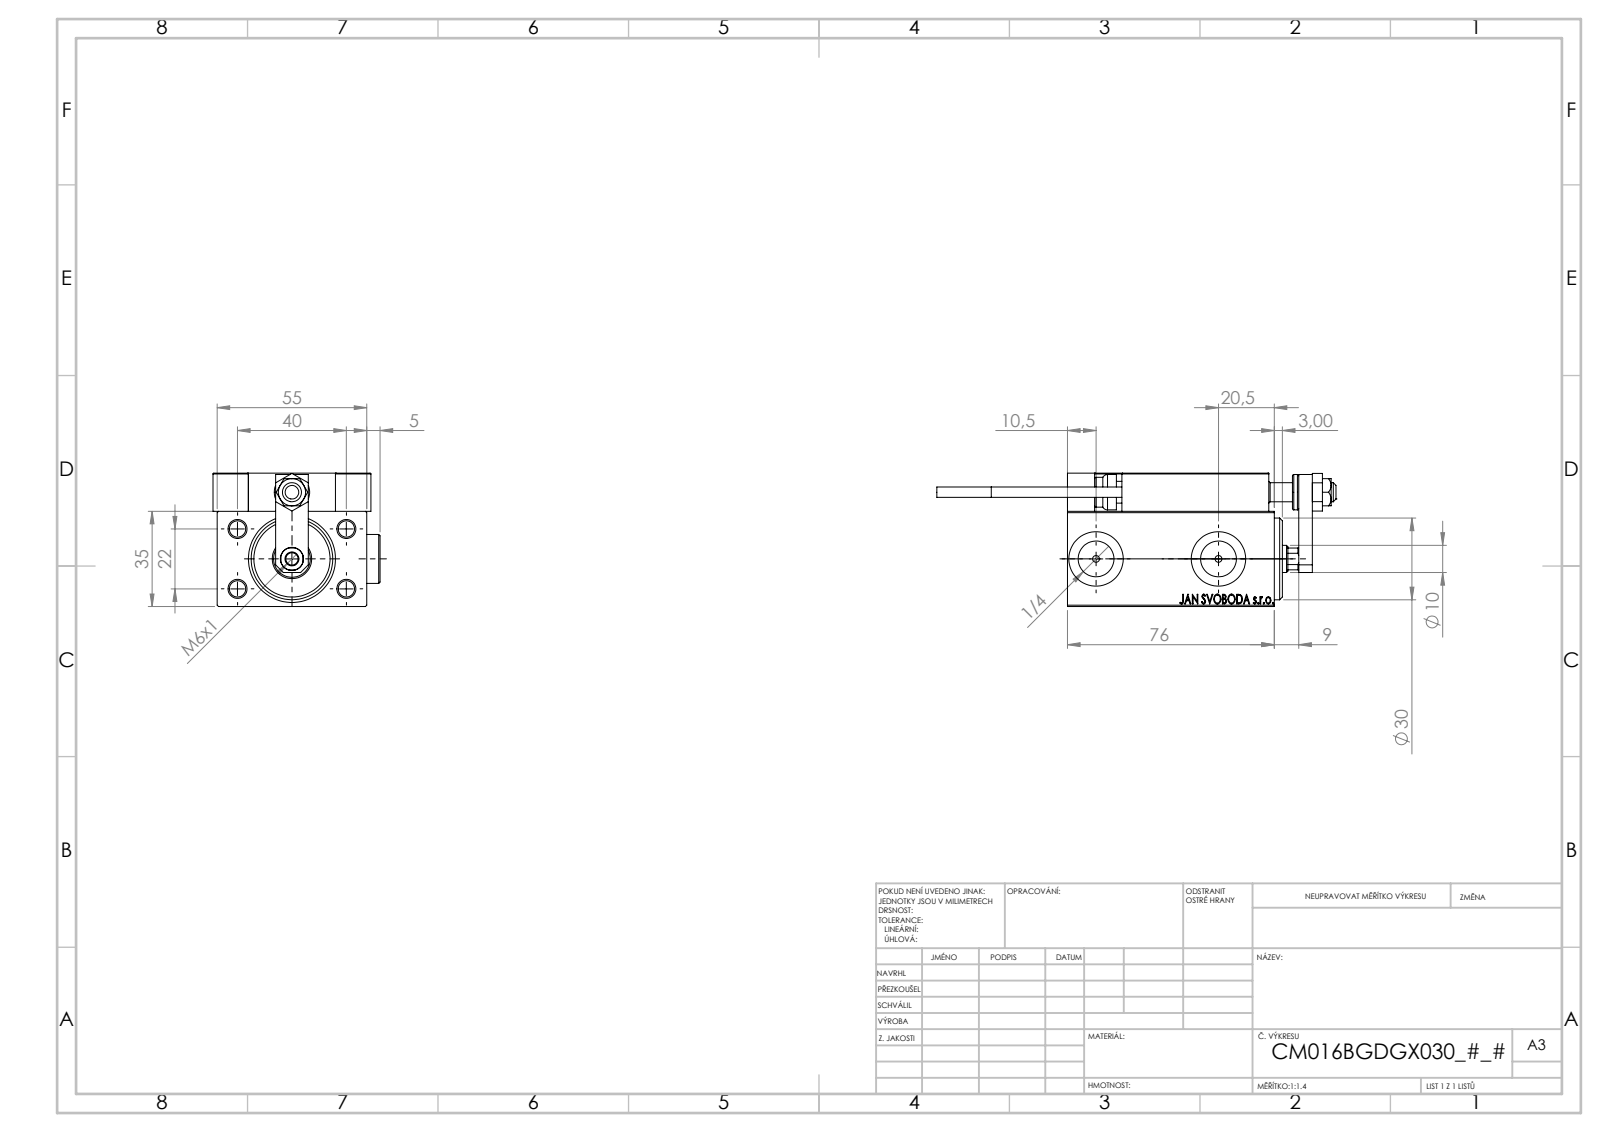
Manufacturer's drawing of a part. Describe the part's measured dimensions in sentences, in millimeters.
The part is named "V450CM_B_Body; V450CM_VC_B; KONCOVKA; Zatka_OIL_PORT (+7 more)". Its 3-D file was written by "SolidWorks 2019 (CONFIG_CONTROL_DESIGN)". It is 26 solids with 1372 faces: 595 planar, 200 cylindrical and 577 other. Overall it measures 146.7 by 61.4 by 49 millimeters. Its volume is 179 831 cubic millimeters and its surface area 55 173 square millimeters. Round holes: 5 of diameter 8, 4 of diameter 3.2, 4 of diameter 4, 4 of diameter 6, 2 of diameter 2.5, 2 of diameter 5, 2 of diameter 13.16, 2 of diameter 20, 1 of diameter 4.5, 1 of diameter 7, 1 of diameter 8.5, 1 of diameter 10. Round bosses or shafts: 2 of diameter 18, 2 of diameter 5, 2 of diameter 3.8, 1 of diameter 13, 1 of diameter 11. Partial cylindrical surfaces (rounded edges, fillets, slot ends): 30 of radius 0.3, 2 of radius 3, 1 of radius 4.5. The main face-to-face distances are 35, 14, 5, 49, 10, 55, 3, 1.5, 7, 13. The hole center spacings are 22.83, 11.37, 20, 22, 24.13, 28.07, 29.59, 29.69.
